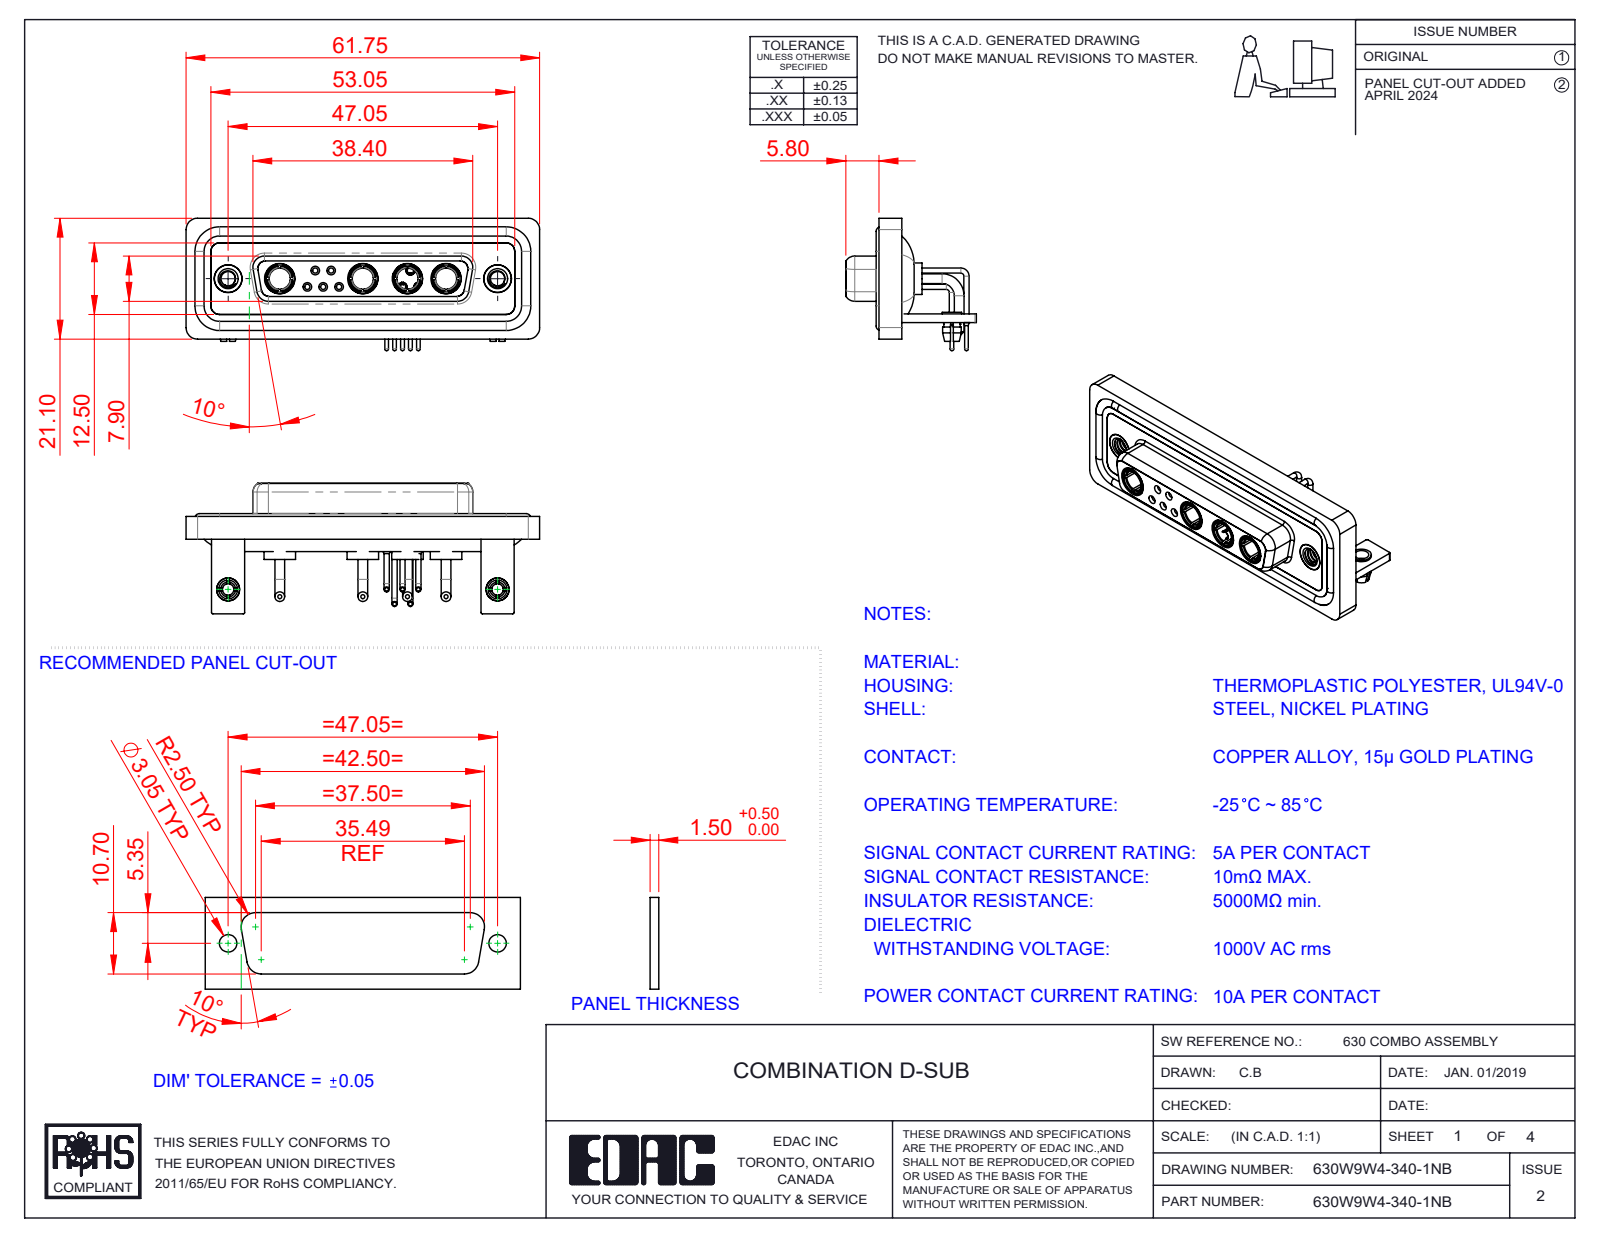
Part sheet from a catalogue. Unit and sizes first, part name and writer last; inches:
Units: inches
Overall size (bounding box): 2.431 × 0.91 × 0.898
Round holes (diameter × count): ⌀0.079 ×7, ⌀0.191 ×6, ⌀0.035 ×5, ⌀0.043 ×5, ⌀0.059 ×5, ⌀0.098 ×4, ⌀0.146 ×4, ⌀0.209 ×4, ⌀0.063 ×3, ⌀0.067 ×2, ⌀0.126 ×2, ⌀0.157 ×2
Round bosses / shafts (diameter × count): ⌀0.035 ×10, ⌀0.063 ×9, ⌀0.067 ×8, ⌀0.079 ×5, ⌀0.059 ×5, ⌀0.026 ×5, ⌀0.217 ×4, ⌀0.205 ×4
Partial cylindrical surfaces — rounded edges, fillets, slot ends (radius × count): R0.079 ×19, R0.059 ×18, R0.01 ×16, R0.053 ×8, R0.063 ×8, R0.02 ×5, R0.024 ×4, R0.026 ×4
Main face-to-face distances: 0.016, 0.071, 0.114, 0.059, 0.146, 0.161, 0.043, 0.055, 0.063, 0.098
Hole centre spacings: 0.124, 0.109, 0.198, 0.545, 0.436, 0.504, 0.61, 0.218
Volume: 0.526 in³ · Surface area: 22.93 in²
Bodies: 24 solids, 1097 faces (364 planar, 457 cylindrical, 276 other)
Part name (STEP PRODUCT): 630Combo Shell Rear_25 Contacts; 630Combo Contact Row 2_50 Contacts; 630Combo Stabilizer Bracket_50 Contacts; 630Combo Board Lock_50 Contacts (+7 more)
STEP written by: SolidWorks 2023 (CONFIG_CONTROL_DESIGN)
